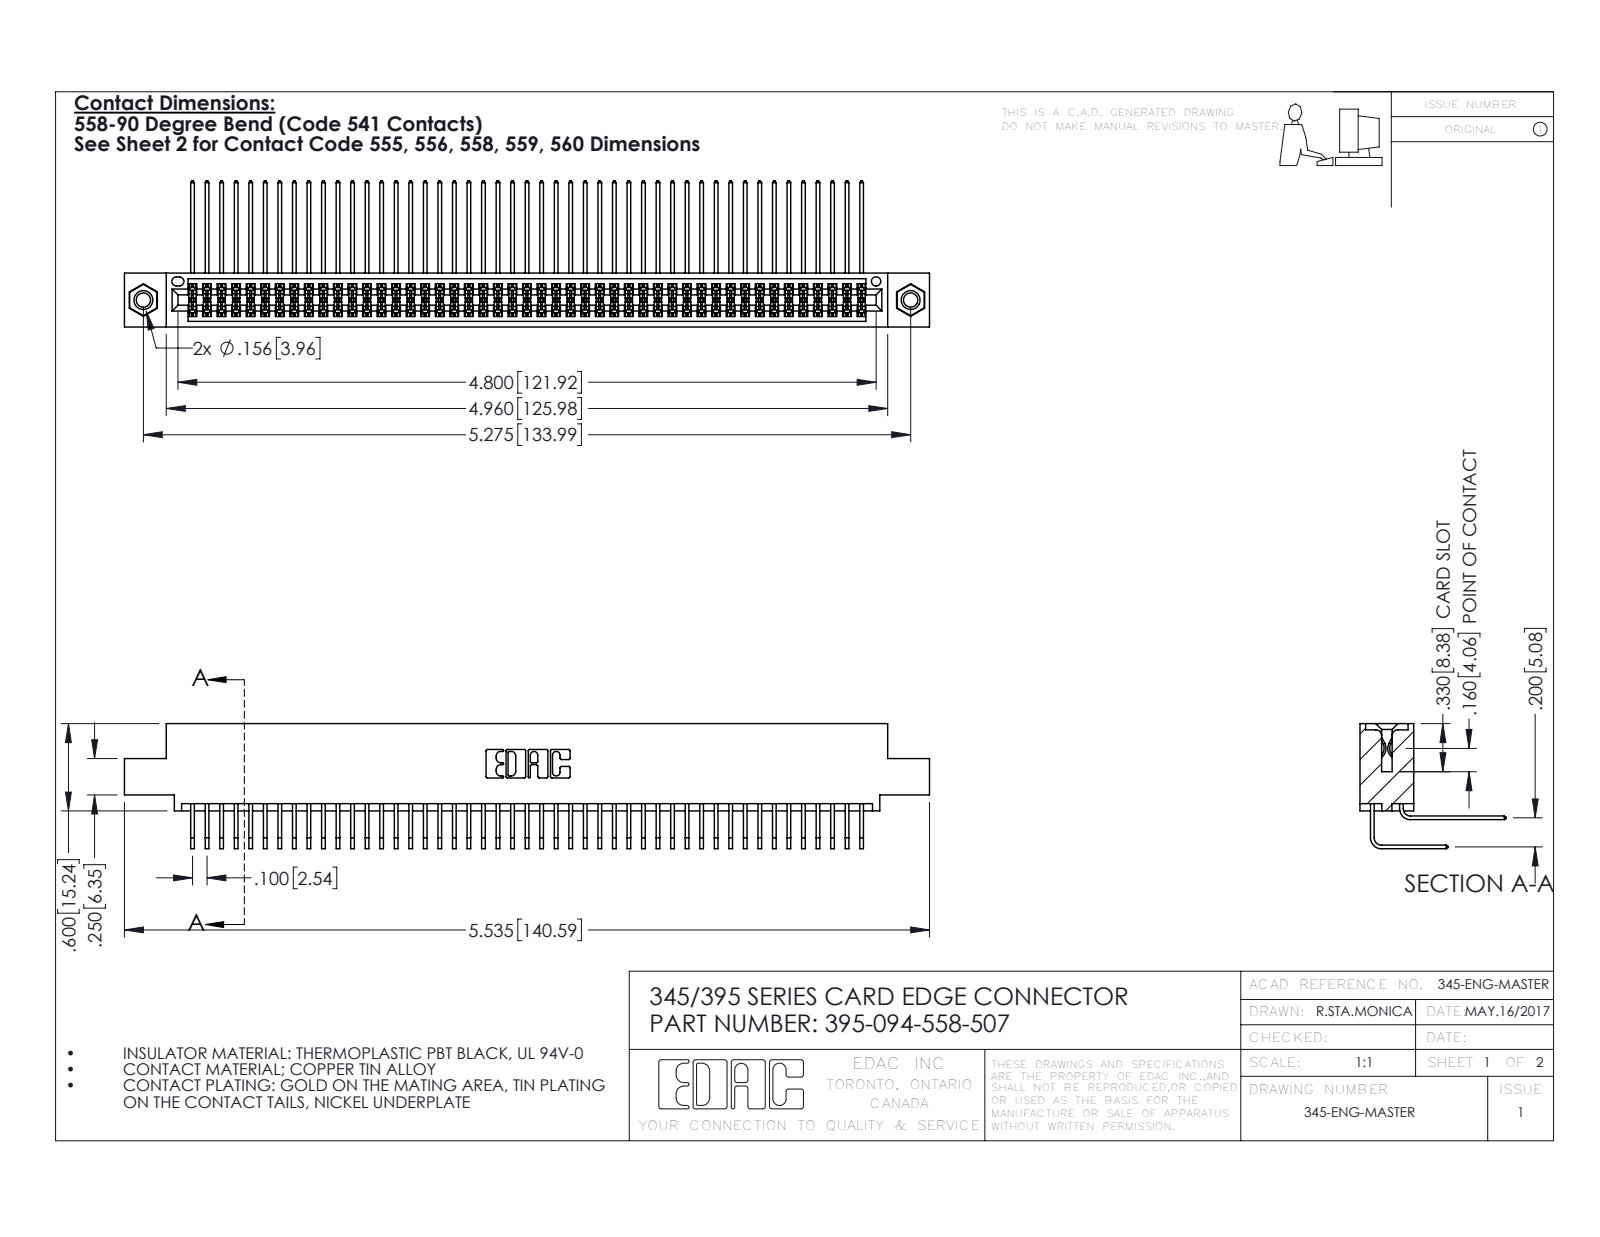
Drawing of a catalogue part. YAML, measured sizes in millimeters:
part_name: "345 Part_0.110 Offset - 0.156 Dia-TI; 395-094-558-507; 345-292-001_558 559 Tail - 1; 345-292-001_558 Tail - 2 (+1 more)"
step_written_by: "SolidWorks 2016 (CONFIG_CONTROL_DESIGN)"
units: millimeters
bodies: {solids: 97, faces: 5078, planar: 3406, cylindrical: 1656, other: 16}
overall_size: [140.6, 25.5, 21.8]
volume: 14200
surface_area: 23700
round_holes:
  - {diameter: 2.5, count: 2}
  - {diameter: 3.2, count: 2}
  - {diameter: 4, count: 2}
  - {diameter: 1.6, count: 1}
round_bosses_or_shafts:
  - {diameter: 3.9, count: 2}
partial_cylinders:
  - {radius: 0.2, count: 142}
  - {radius: 0.3, count: 22}
  - {radius: 0.2, count: 6}
  - {radius: 0.8, count: 6}
  - {radius: 0.7, count: 3}
  - {radius: 0.4, count: 2}
  - {radius: 0.5, count: 2}
  - {radius: 0.6, count: 2}
face_to_face_distances: [1.8, 7.6, 5.1, 9.4, 2.5, 6.9, 0.6, 5.7, 0.6, 4.4]
hole_center_spacings: [6.9, 128, 134]
